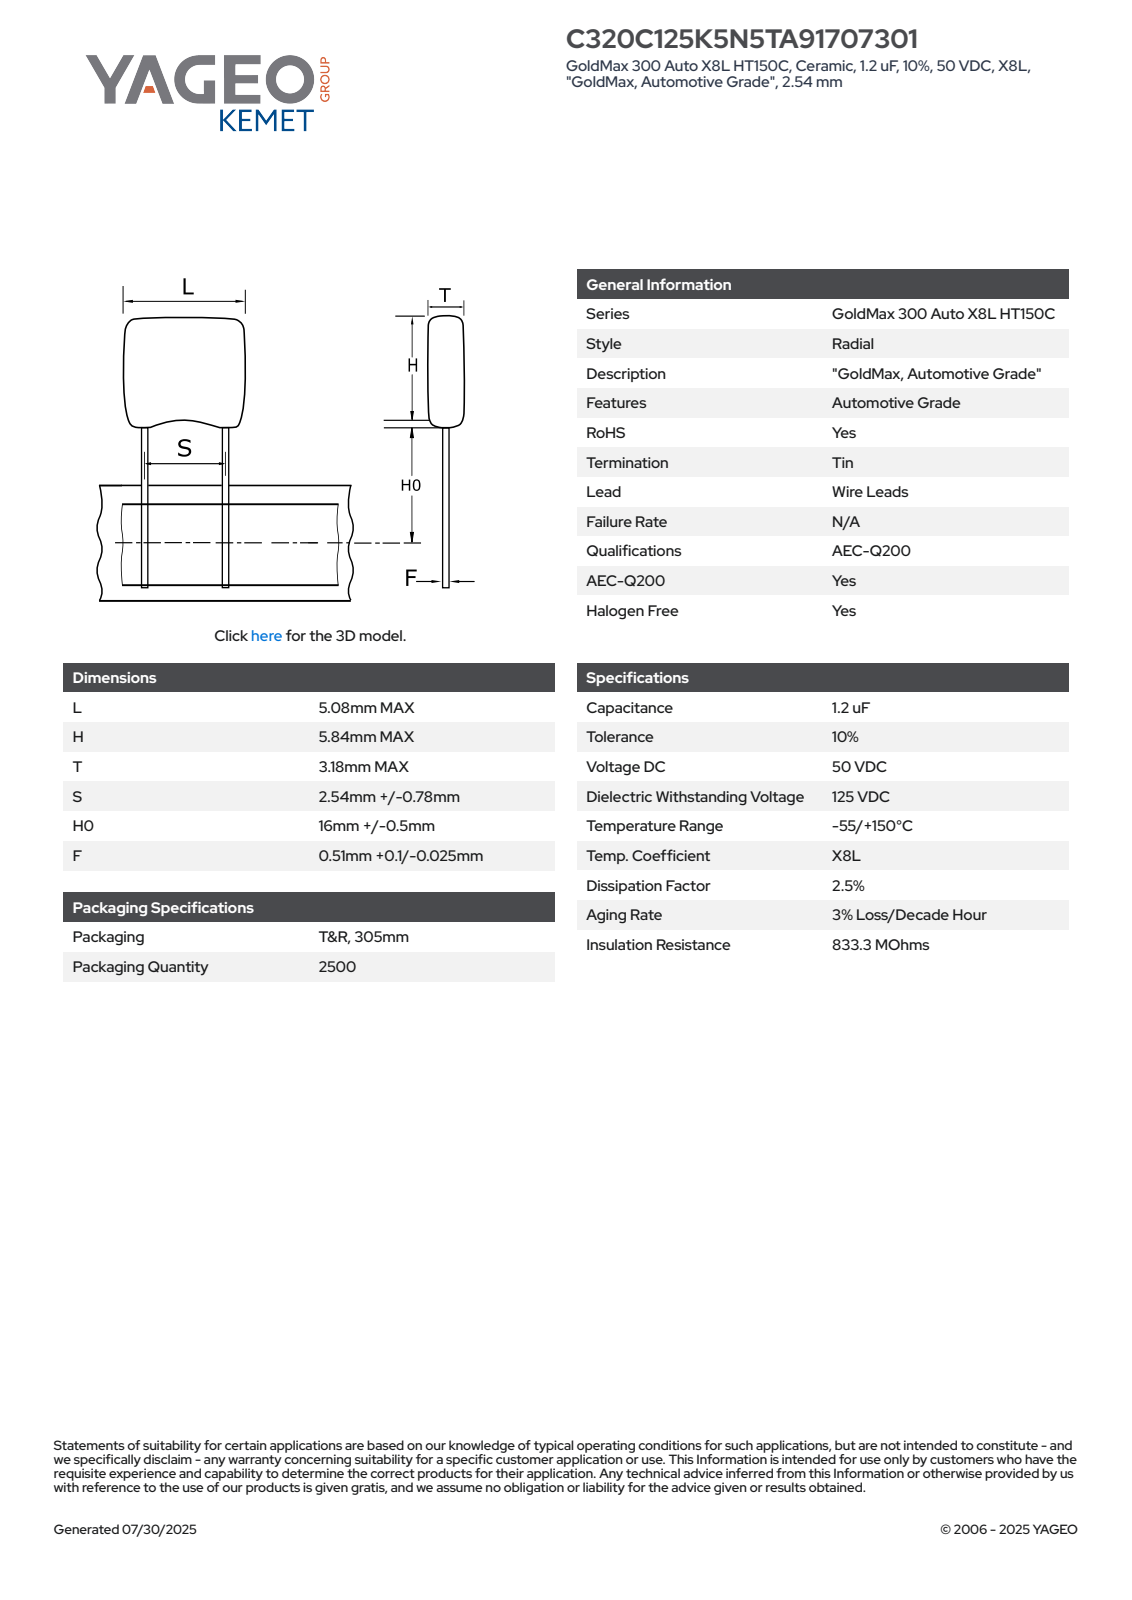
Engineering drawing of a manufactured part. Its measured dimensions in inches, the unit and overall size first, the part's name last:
Units: inches
Overall size (bounding box): 0.906 × 0.2 × 0.126
Round bosses / shafts (diameter × count): ⌀0.024 ×2
Partial cylindrical surfaces — rounded edges, fillets, slot ends (radius × count): R0.03 ×12
Main face-to-face distances: 0.125, 0.2, 0.256, 0.65, 0.906, 0.126, 0.783, 0.134, 0.122, 0.763
Volume: 0.006 in³ · Surface area: 0.29 in²
Bodies: 4 solids, 92 faces (66 planar, 16 cylindrical, 10 other)
Part name (STEP PRODUCT): CCR_KRCST_C320_L5.08H5.84T3.18S2.54H016.5F0.61
STEP written by: SolidWorks 2014 (AUTOMOTIVE_DESIGN)
